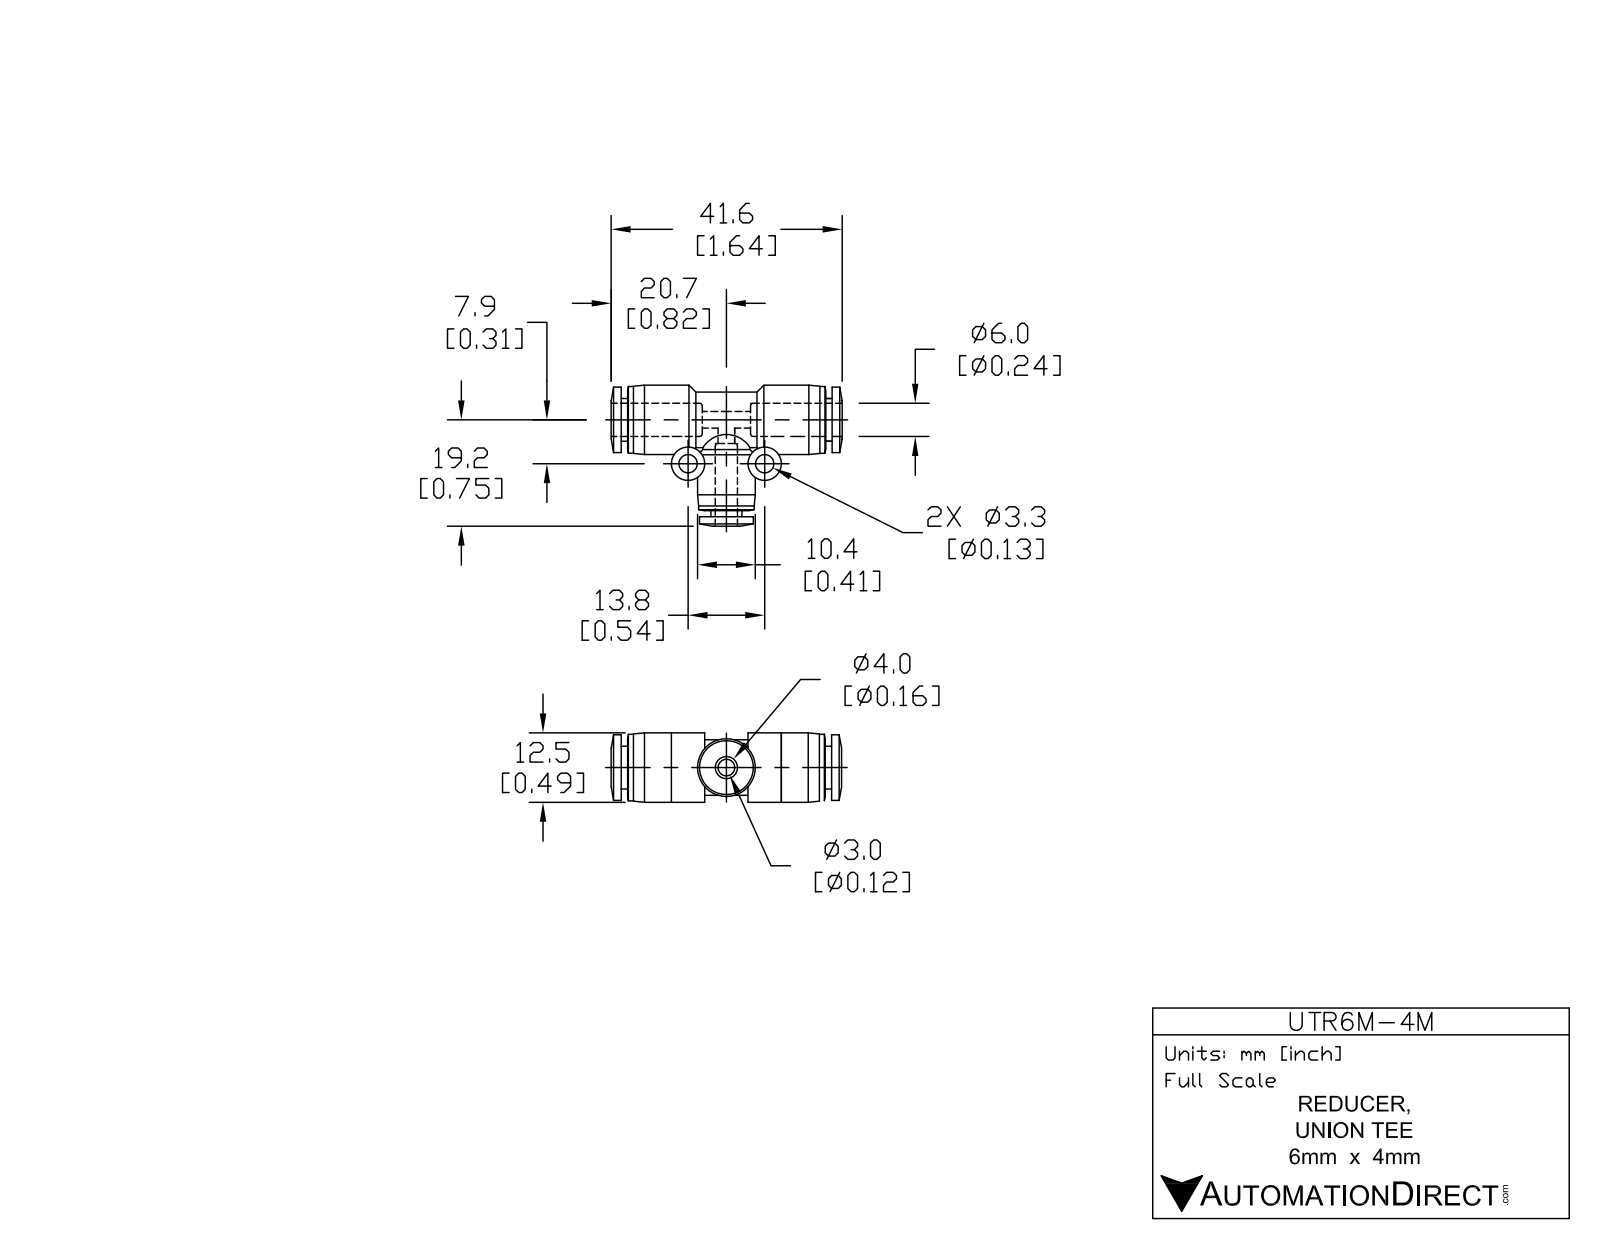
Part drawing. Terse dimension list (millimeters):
name: UTR6M-4M
written by: SolidWorks 2015 (AUTOMOTIVE_DESIGN)
unit: mm
bodies: 1 solid, 94 faces (18 planar, 46 cylindrical, 30 other)
size: 41.5 × 25.2 × 12.5
volume: 4 440 mm³; area: 4 042 mm²
holes: 2× ⌀3, 2× ⌀3.3, 1× ⌀4.3, 1× ⌀6.3
bosses: 2× ⌀10, 2× ⌀6, 1× ⌀12.5, 1× ⌀12, 1× ⌀11.8, 1× ⌀10.4, 1× ⌀9.7, 1× ⌀8.5
face distances: 1.1, 36.8, 37.9, 14.6, 23.3, 13.5, 22.1, 12.5, 35.6, 1.1
hole spacings: 13.8
